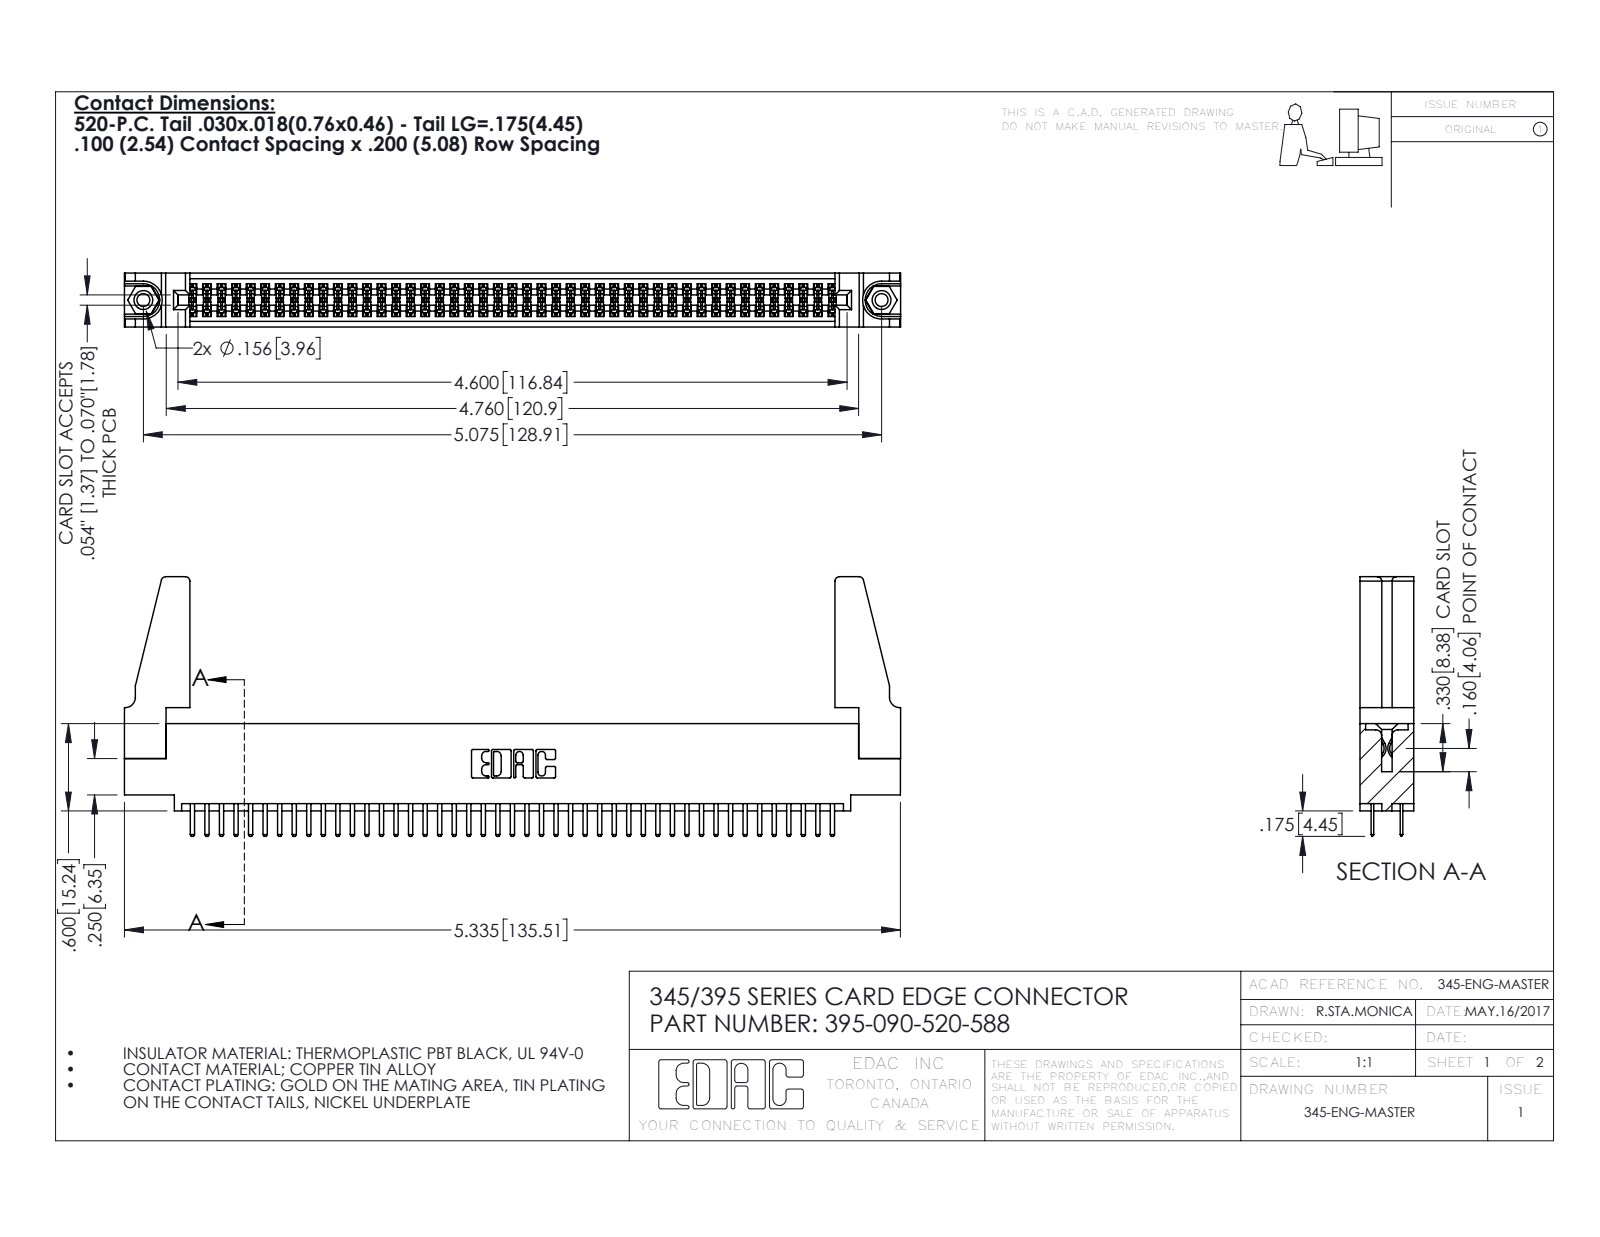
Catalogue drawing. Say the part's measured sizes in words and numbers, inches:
The part is named "345-220-078_345-220-088; 395-090-520-588; 345-292-001_345-293-120; 345-250-001_345-250-001-102 (+1 more)". Its 3-D file was written by "SolidWorks 2016 (CONFIG_CONTROL_DESIGN)". It is 95 solids with 5114 faces: 3306 planar, 1792 cylindrical and 16 other. Overall it measures 5.336 by 1.785 by 0.37 inches. Its volume is 0.997 cubic inches and its surface area 34.91 square inches. Round holes: 2 of diameter 0.089, 2 of diameter 0.125, 2 of diameter 0.156, 1 of diameter 0.064. Round bosses or shafts: 2 of diameter 0.155. Partial cylindrical surfaces (rounded edges, fillets, slot ends): 135 of radius 0.006, 94 of radius 0.01, 22 of radius 0.01, 8 of radius 0.03, 6 of radius 0.007, 6 of radius 0.031, 3 of radius 0.026, 2 of radius 0.014. The main face-to-face distances are 0.072, 0.298, 0.37, 0.2, 0.098, 0.272, 0.025, 0.225, 0.022, 0.072. The hole center spacings are 0.27, 4.839, 5.075.
